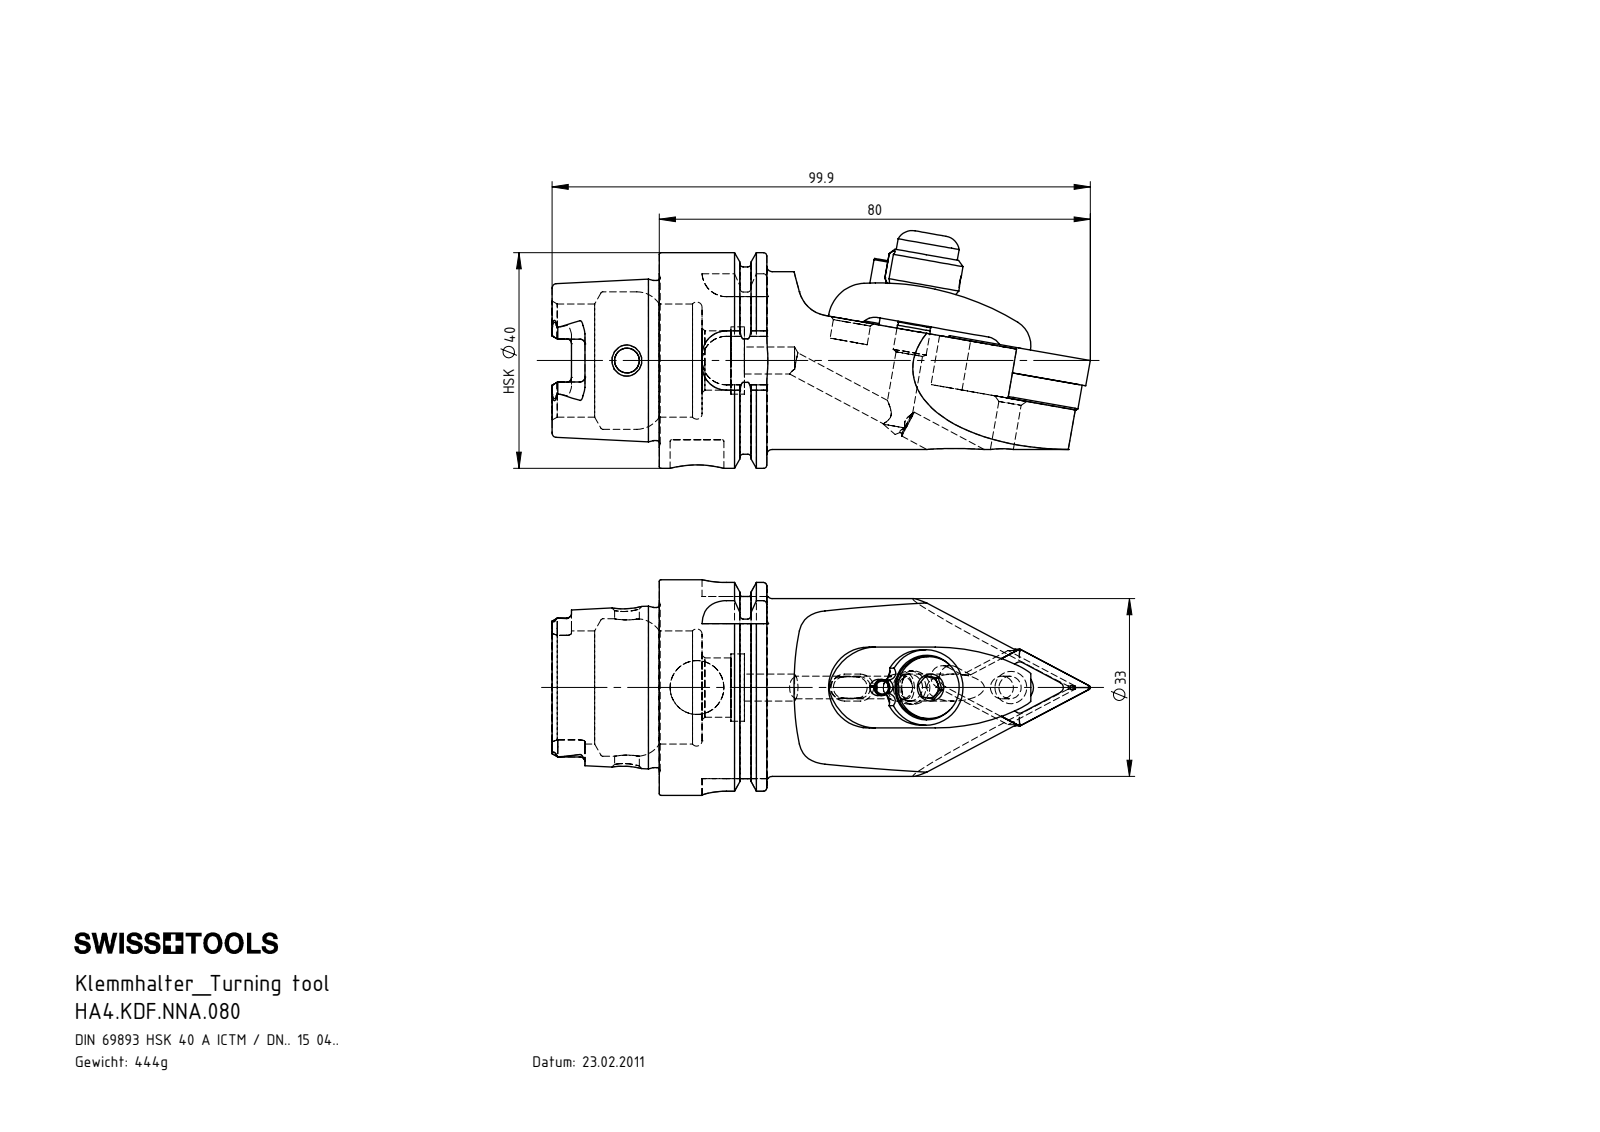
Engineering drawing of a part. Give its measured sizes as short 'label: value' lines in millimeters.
name: HA4.KDF.NNA.080; WCC-ER5.102.012_B; WDF-ER2.101.003_A; WCC-ER2.001.010_A (+6 more)
written by: SolidWorks 2022 (AUTOMOTIVE_DESIGN)
unit: mm
bodies: 10 solids, 451 faces (119 planar, 149 cylindrical, 183 other)
size: 99.9 × 44.16 × 40
volume: 55 788 mm³; area: 20 181 mm²
holes: 3× ⌀2, 2× ⌀4.2, 2× ⌀5, 2× ⌀7, 1× ⌀3, 1× ⌀4, 1× ⌀4.6, 1× ⌀5.16, 1× ⌀6.2, 1× ⌀6.5, 1× ⌀8.5, 1× ⌀10
bosses: 2× ⌀5, 1× ⌀40, 1× ⌀34.75, 1× ⌀33, 1× ⌀29.71, 1× ⌀14, 1× ⌀11.5, 1× ⌀7
rounds: 6× R0.39, 6× R0.69, 6× R0.9, 4× R0.4, 4× R1.88, 4× R4.5, 3× R1.5, 3× R3
face distances: 12.3, 6.05, 7.34, 1.29, 12.7, 0.4, 9.22, 7.95, 12, 19.95
hole spacings: 20, 20.01, 7.99, 8, 8.2, 19.8, 19.81, 28
